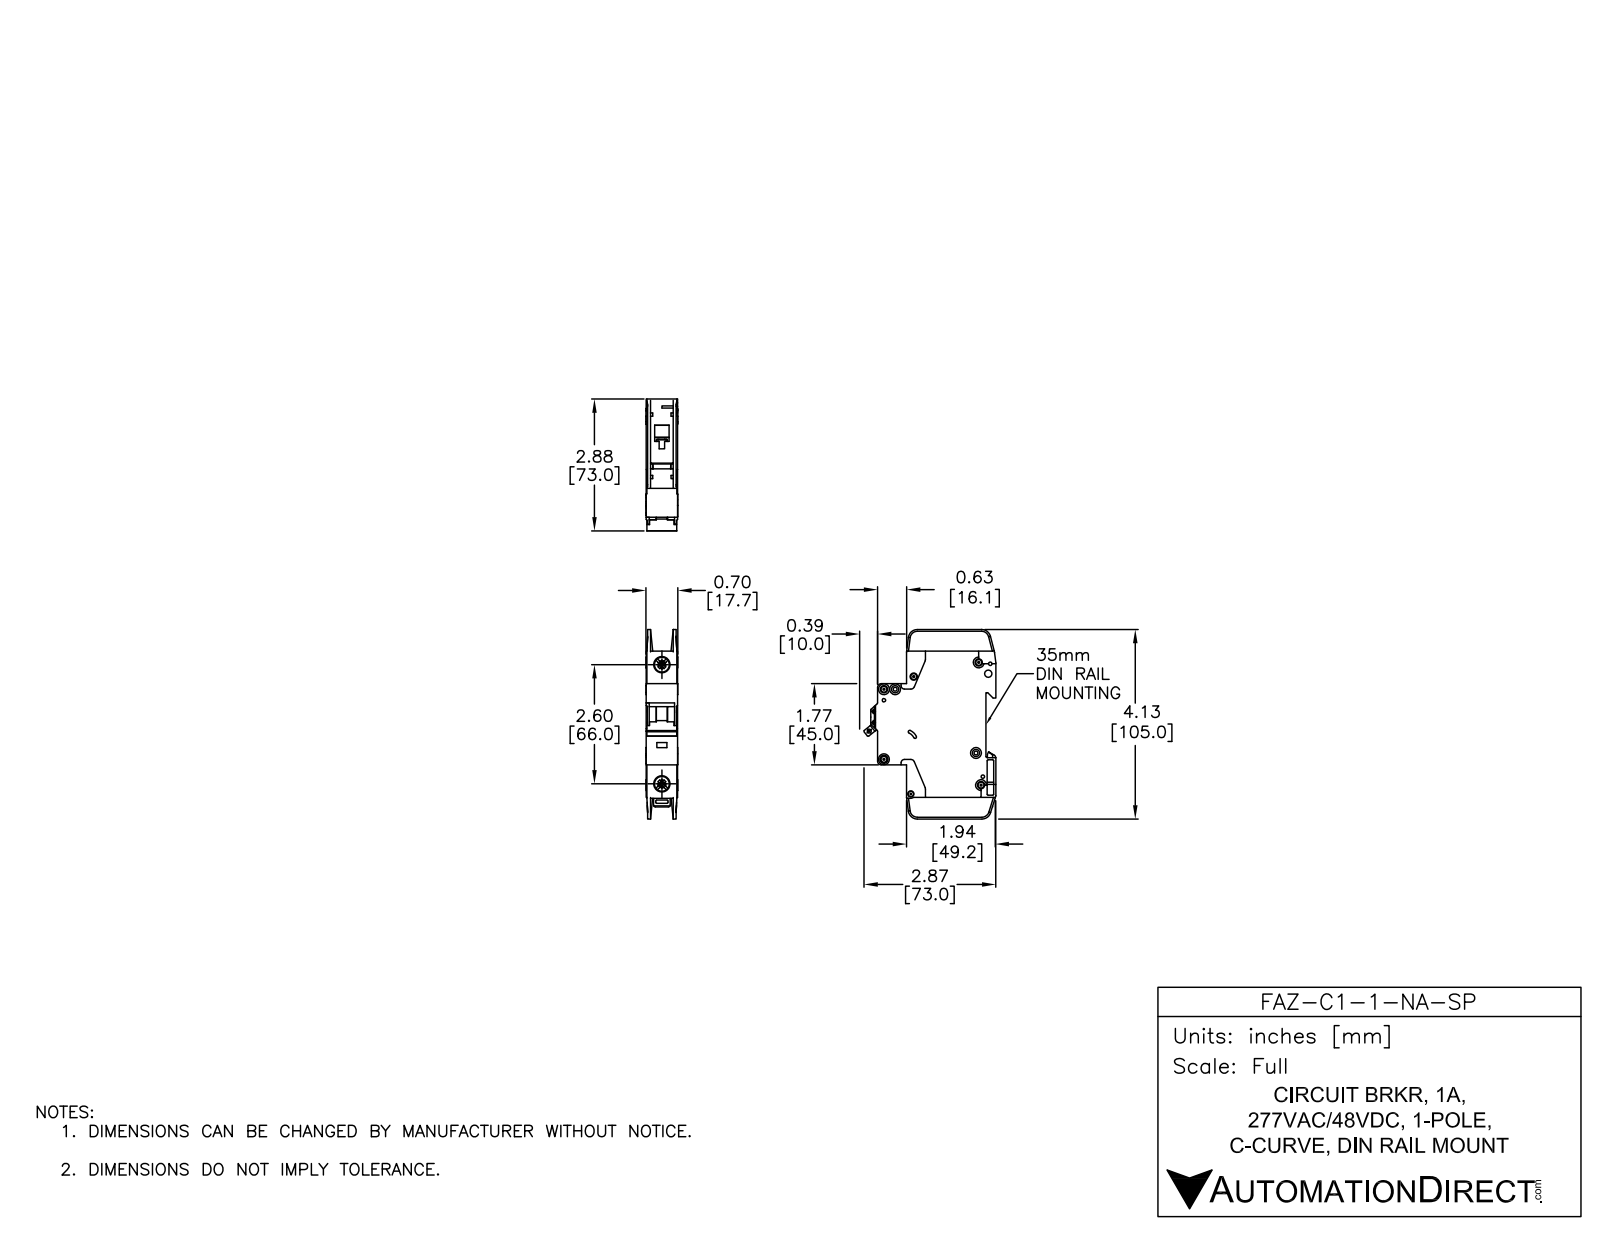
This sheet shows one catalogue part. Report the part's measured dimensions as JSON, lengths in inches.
{"part_name": "FAZ-C1-1-NA-SP", "step_written_by": "SolidWorks 2014 (AUTOMOTIVE_DESIGN)", "units": "inches", "bodies": {"solids": 3, "faces": 784, "planar": 409, "cylindrical": 263, "other": 112}, "overall_size": [4.134, 2.876, 0.697], "volume_in3": 4.741, "surface_area_in2": 38.35, "round_holes": [[0.142, 7], [0.043, 2], [0.059, 2], [0.157, 2], [0.281, 2], [0.323, 2], [0.075, 1], [0.085, 1], [0.087, 1], [0.1, 1], [0.13, 1], [0.134, 1]], "round_bosses_or_shafts": [[0.236, 7], [0.098, 1]], "partial_cylinders_radius": [[0.01, 29], [0.02, 18], [0.039, 10], [0.079, 10], [0.197, 5], [0.157, 4], [0.071, 3], [0.008, 2]], "face_to_face_distances": [0.689, 0.593, 0.028, 0.096, 0.069, 0.62, 0.524, 0.551, 0.496, 0.079], "hole_center_spacings": [0.244, 0.204, 0.24, 0.322, 0.337, 0.343, 0.437, 0.49]}
